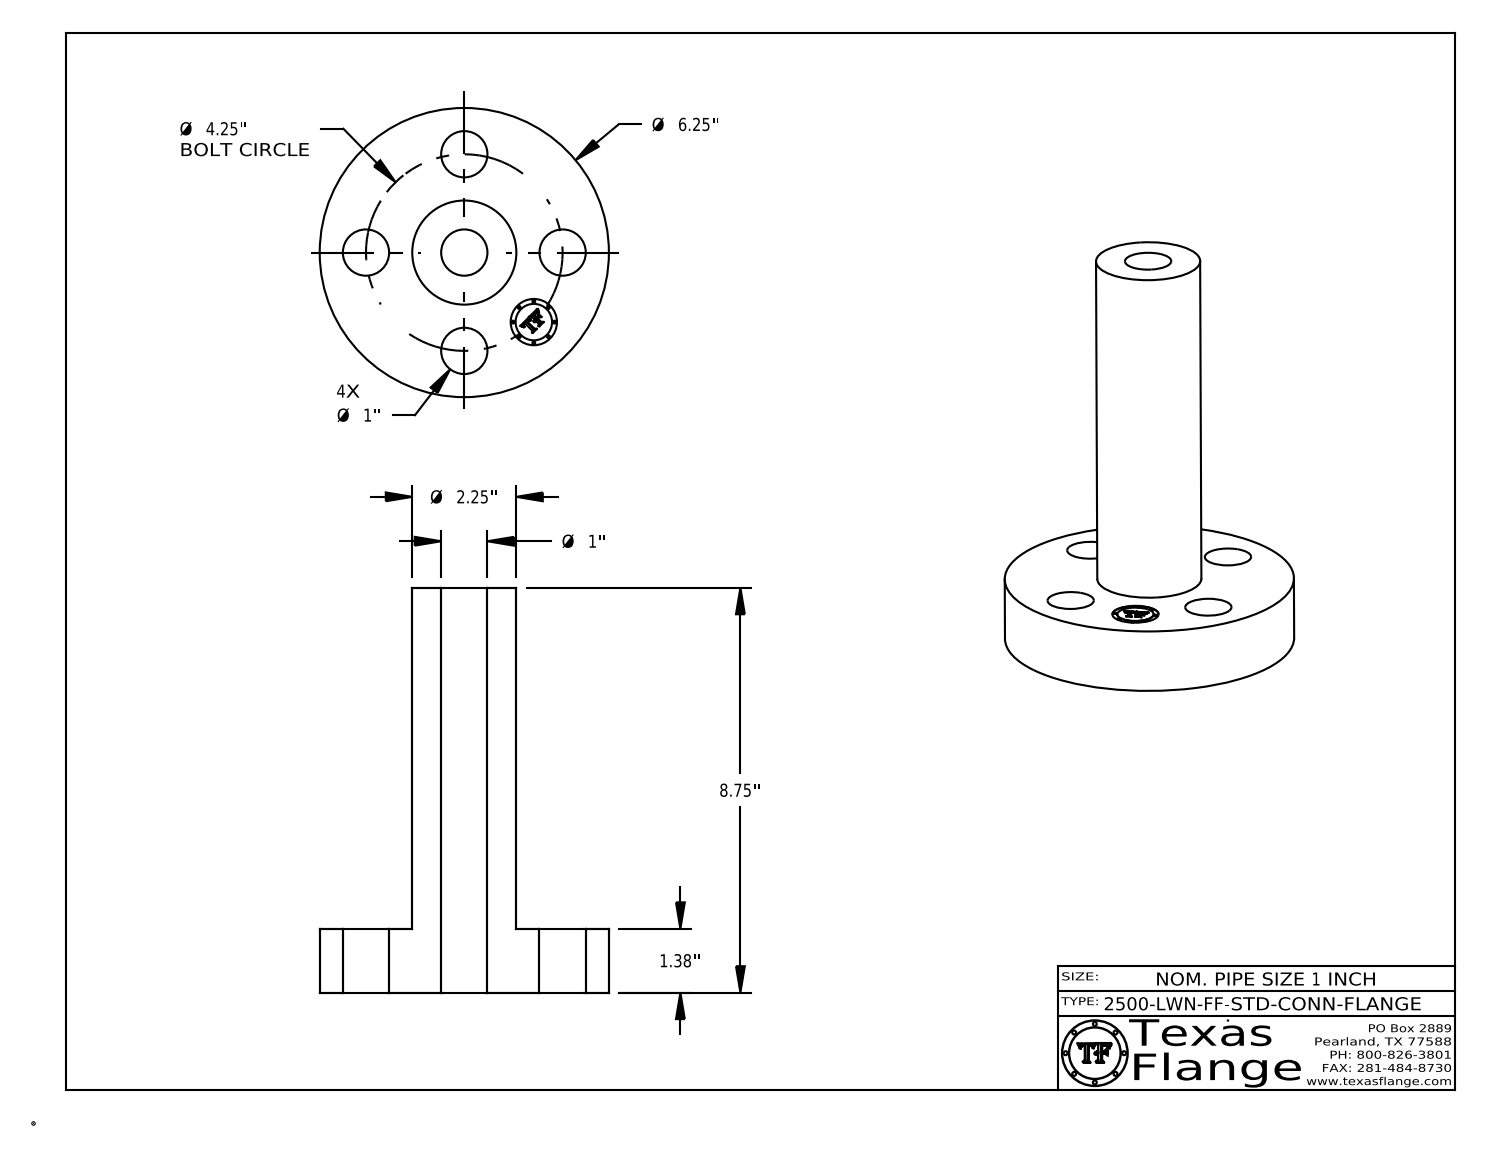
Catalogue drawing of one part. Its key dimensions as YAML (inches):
part_name: "1-2500-LWN-FF-STD-CONN-FLANGE"
step_written_by: "CATIA V5 STEP AP214 (AUTOMOTIVE_DESIGN)"
units: inches
bodies: {solids: 1, faces: 402, planar: 368, cylindrical: 34, other: 0}
overall_size: [8.75, 6.25, 6.25]
volume: 60.43
surface_area: 177.6
round_holes:
  - {diameter: 1, count: 6}
round_bosses_or_shafts:
  - {diameter: 0.061, count: 8}
  - {diameter: 6.25, count: 1}
  - {diameter: 2.25, count: 1}
  - {diameter: 0.788, count: 1}
face_to_face_distances: [1.38, 8.75, 7.37, 1.375, 7.375, 0.298, 0.292, 0.054, 0.193, 0.248]
hole_center_spacings: [2.125, 3.006, 1.626, 3.927, 4.25]
